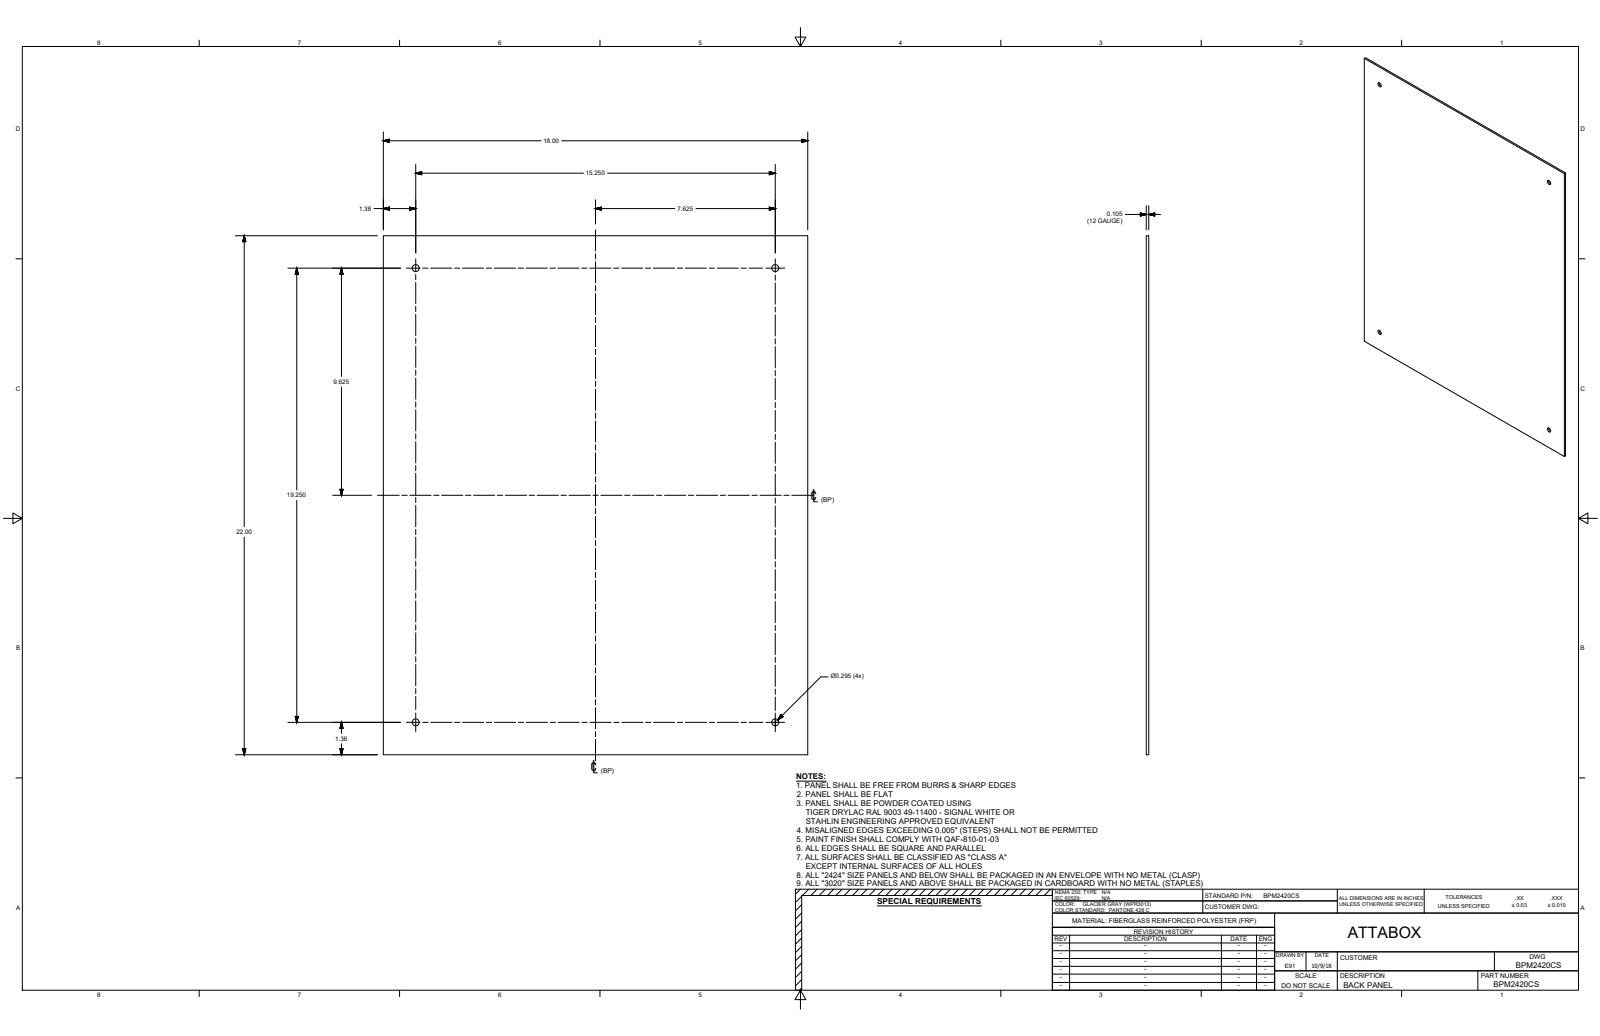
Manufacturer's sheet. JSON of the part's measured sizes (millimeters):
{"part_name": "HW-MP2420CS", "step_written_by": "Autodesk Inventor 2017 (CONFIG_CONTROL_DESIGN)", "units": "millimeters", "bodies": {"solids": 1, "faces": 10, "planar": 6, "cylindrical": 4, "other": 0}, "overall_size": [558.8, 558.8, 2.67], "volume_mm3": 832320, "surface_area_mm2": 630375, "round_holes": [[7.49, 4]], "face_to_face_distances": [2.67, 558.8], "hole_center_spacings": [488.96, 691.49]}
